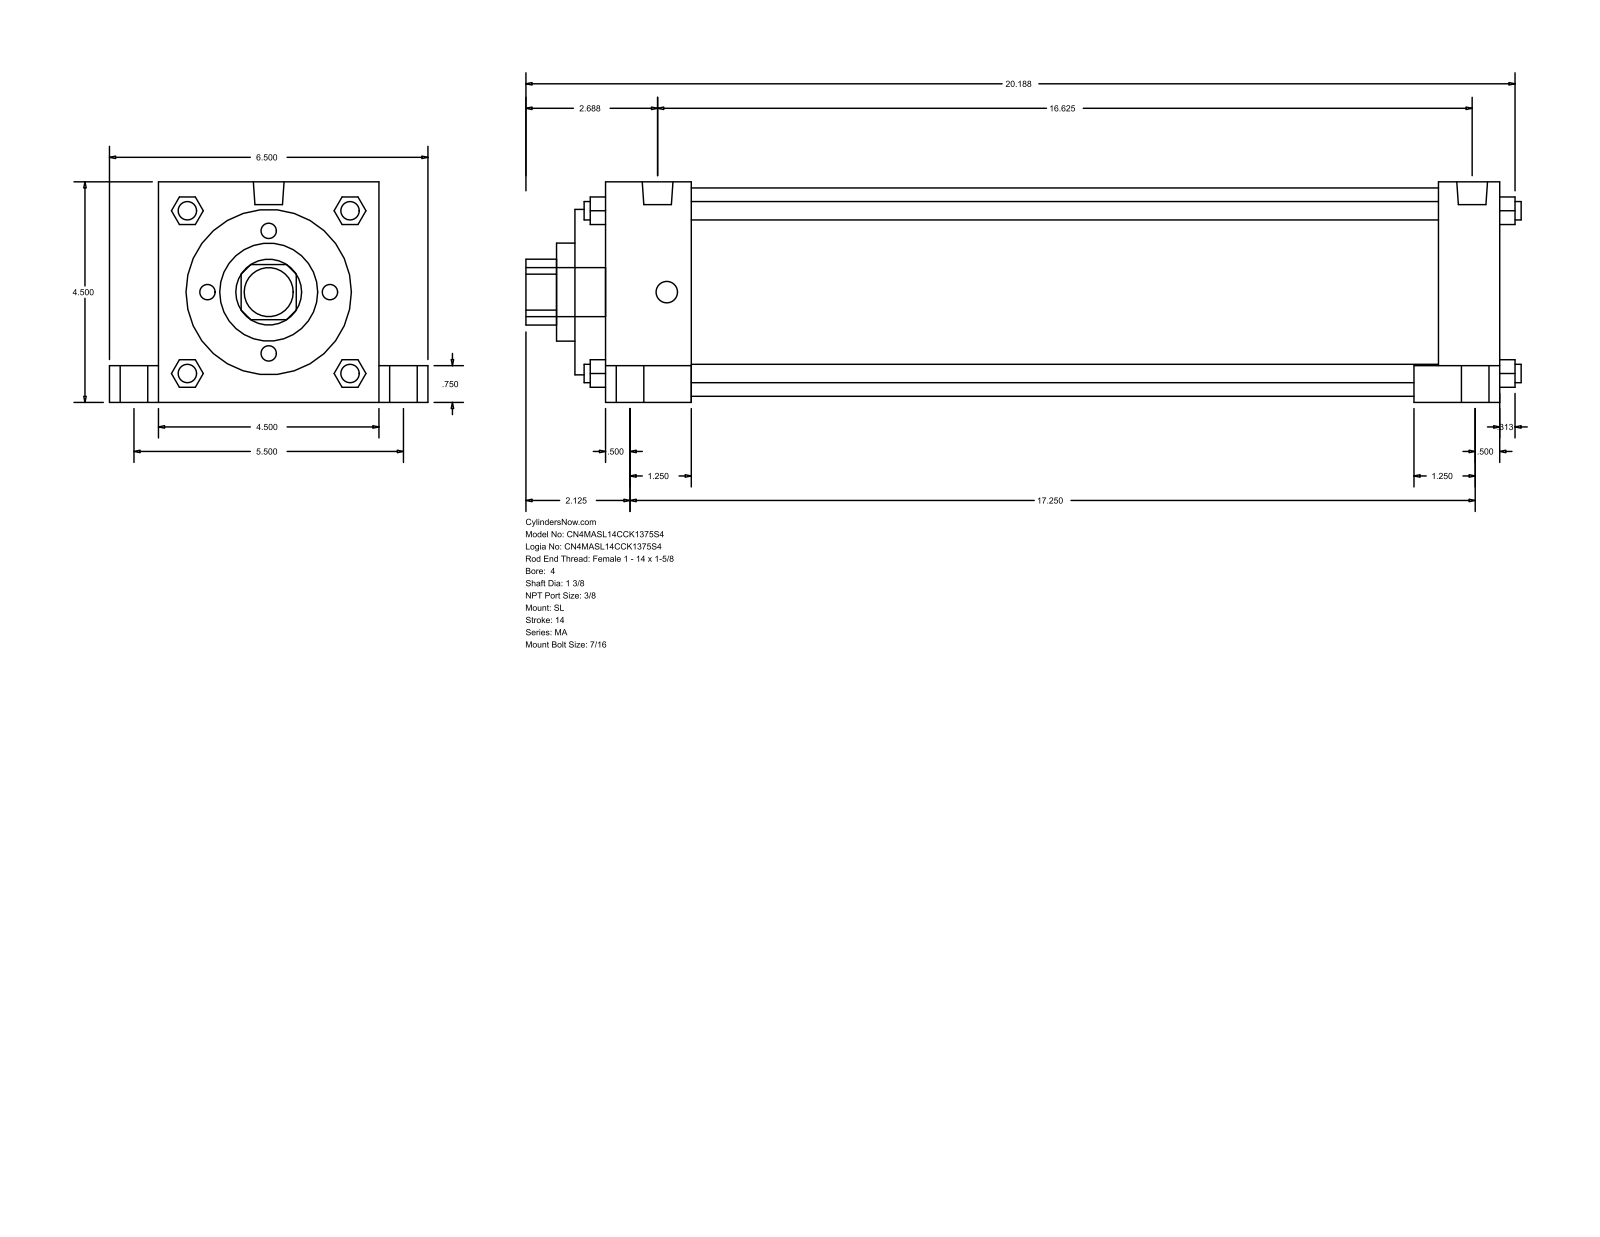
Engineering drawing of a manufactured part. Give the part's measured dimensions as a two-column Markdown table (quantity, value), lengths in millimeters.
| quantity | value |
| --- | --- |
| part name | MA_SL__0400_1.375 |
| STEP written by | GSSL Pune (CONFIG_CONTROL_DESIGN) |
| units | millimeters |
| bodies | 0 solids, 150 faces (113 planar, 37 cylindrical, 0 other) |
| overall size | 515.94 × 165.1 × 114.3 |
| round holes (diameter × count) | 34.92 × 1, 50.8 × 1, 85.72 × 1, 107.95 × 1 |
| round bosses / shafts (diameter × count) | 20.64 × 4, 14.29 × 4, 11.11 × 4, 9.53 × 4, 15.93 × 2, 25.4 × 1 |
| partial cylindrical surfaces (radius × count) | 17.06 × 1 |
| main face-to-face distances | 114.3, 463.55, 387.35, 479.42, 15.87, 60.32, 44.45, 419.1, 447.67, 431.8 |
